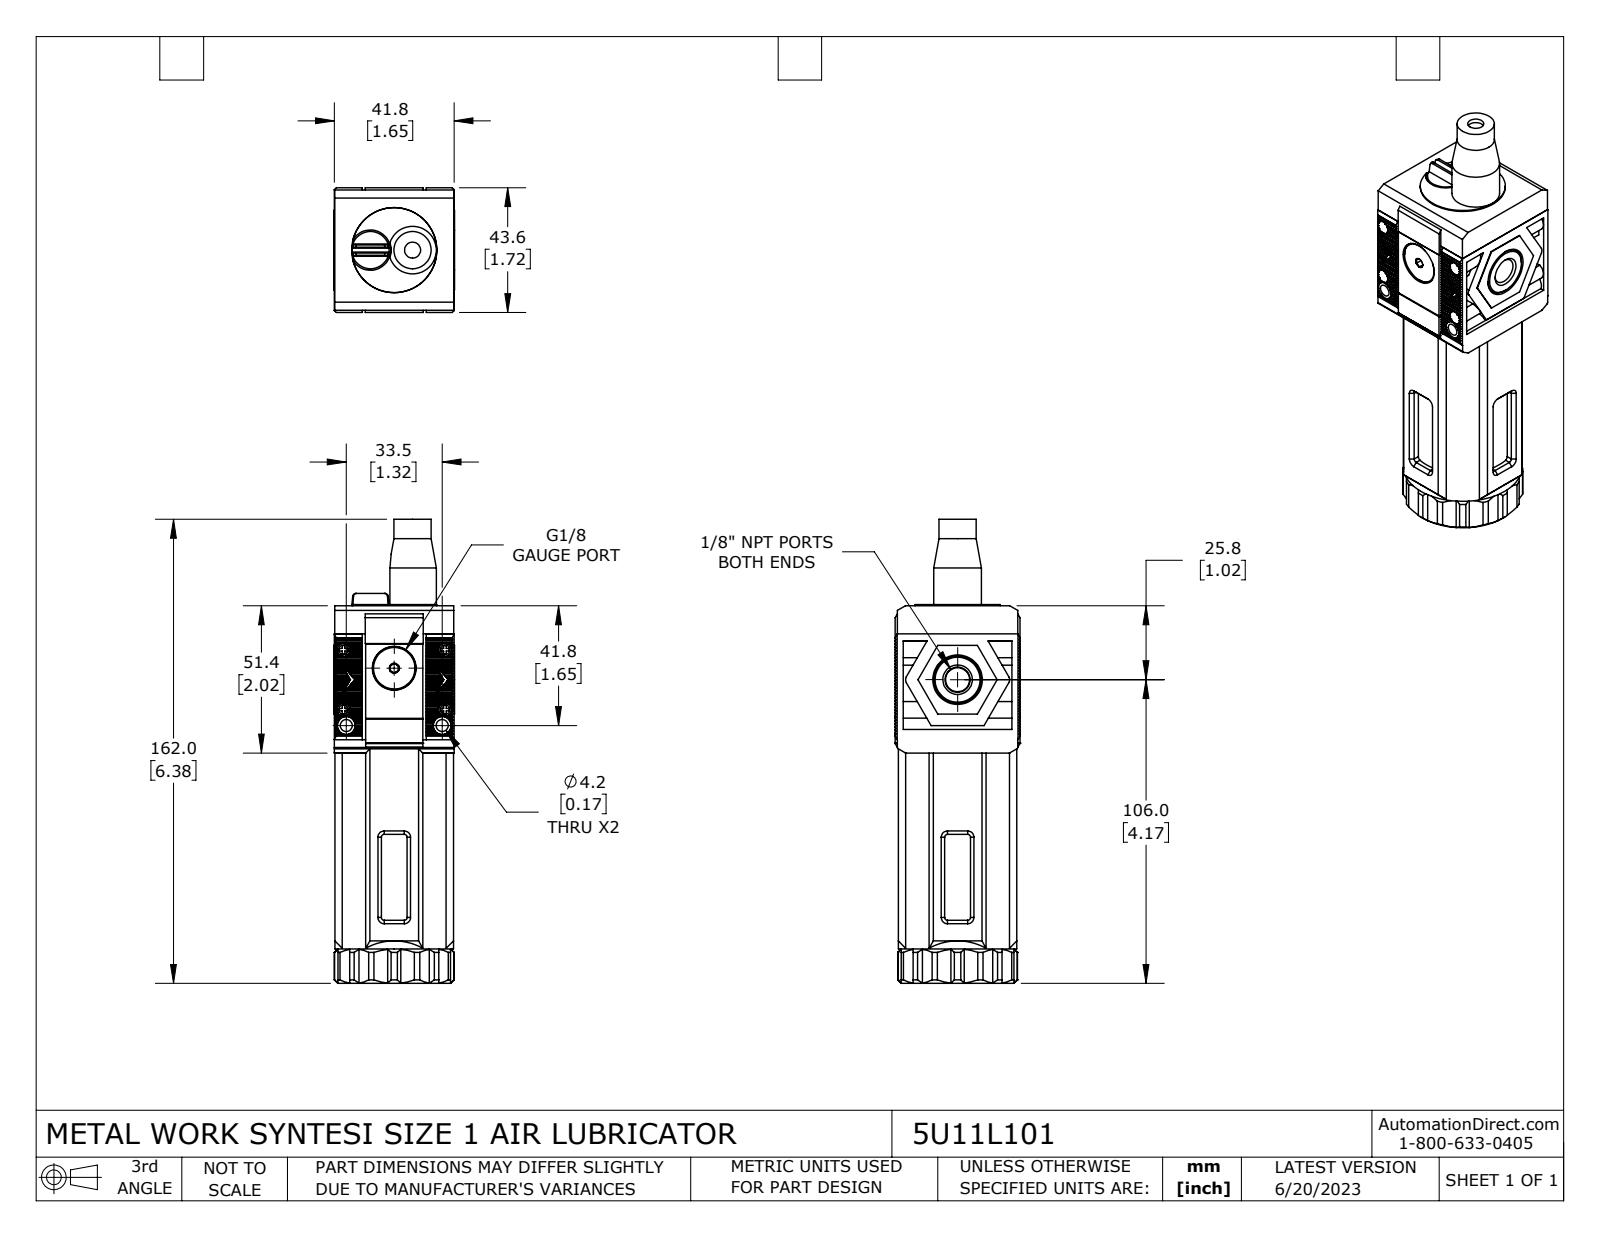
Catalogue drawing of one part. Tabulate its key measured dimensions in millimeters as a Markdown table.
| quantity | value |
| --- | --- |
| part name | 5U11L101 |
| STEP written by | SolidWorks 2021 (CONFIG_CONTROL_DESIGN) |
| units | millimeters |
| bodies | 14 solids, 1343 faces (921 planar, 262 cylindrical, 160 other) |
| overall size | 162 × 43.6 × 42.2 |
| volume | 135 900 mm³ |
| surface area | 65 550 mm² |
| round holes (diameter × count) | 2.1 × 4, 3 × 4, 4.7 × 4, 4.2 × 2, 5.6 × 1, 8.6 × 1, 14.1 × 1, 15.3 × 1, 29.7 × 1, 30 × 1, 31.3 × 1, 34 × 1 |
| round bosses / shafts (diameter × count) | 4.6 × 4, 2.6 × 4, 13 × 2, 6.2 × 2, 41.4 × 1, 35.6 × 1, 25 × 1, 22.8 × 1 |
| partial cylindrical surfaces (radius × count) | 1 × 8, 0.6 × 4, 3.1 × 4, 0.2 × 2, 2 × 2, 7.2 × 1, 11 × 1, 20.9 × 1 |
| main face-to-face distances | 41.6, 41.4, 1.1, 42.5, 7.6, 41.8, 33.8, 34, 7.8, 40 |
| hole center spacings | 5.6, 18.8, 20.9, 22.9, 26.1, 26.5, 34.9, 35.4 |
